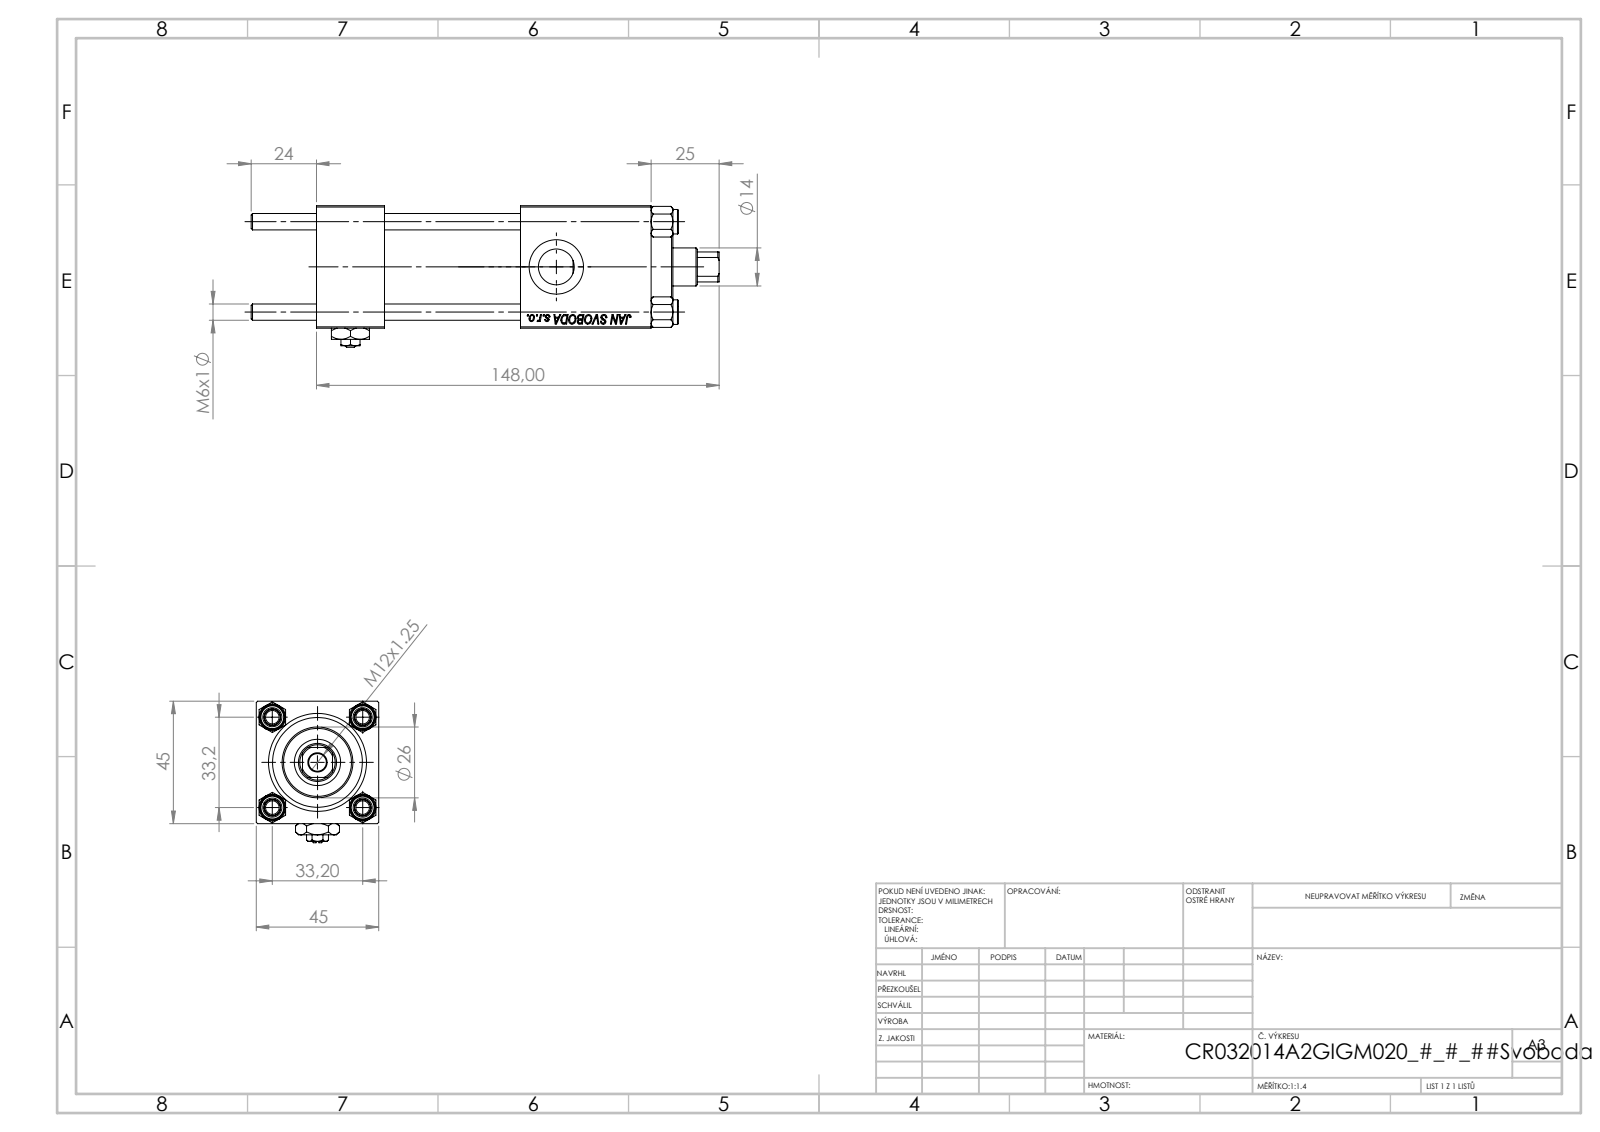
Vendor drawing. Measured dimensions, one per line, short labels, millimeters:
name: NUT_M5; V215CR_BODY_A; Zatka_pro_OIL_PORT; V215CR_VCP (+2 more)
written by: SolidWorks 2019 (CONFIG_CONTROL_DESIGN)
unit: mm
bodies: 12 solids, 1184 faces (542 planar, 84 cylindrical, 558 other)
size: 172 × 52 × 45
volume: 197 465 mm³; area: 73 894 mm²
holes: 4× ⌀6, 2× ⌀7, 2× ⌀13.16, 2× ⌀20, 1× ⌀6.5, 1× ⌀14, 1× ⌀17, 1× ⌀24, 1× ⌀32, 1× ⌀33
bosses: 4× ⌀9, 1× ⌀38, 1× ⌀26
rounds: 1× R6.5
face distances: 45, 25, 123, 98, 50, 75, 48, 94.3, 69.3, 19.3
hole spacings: 23.48, 33.2, 46.95
